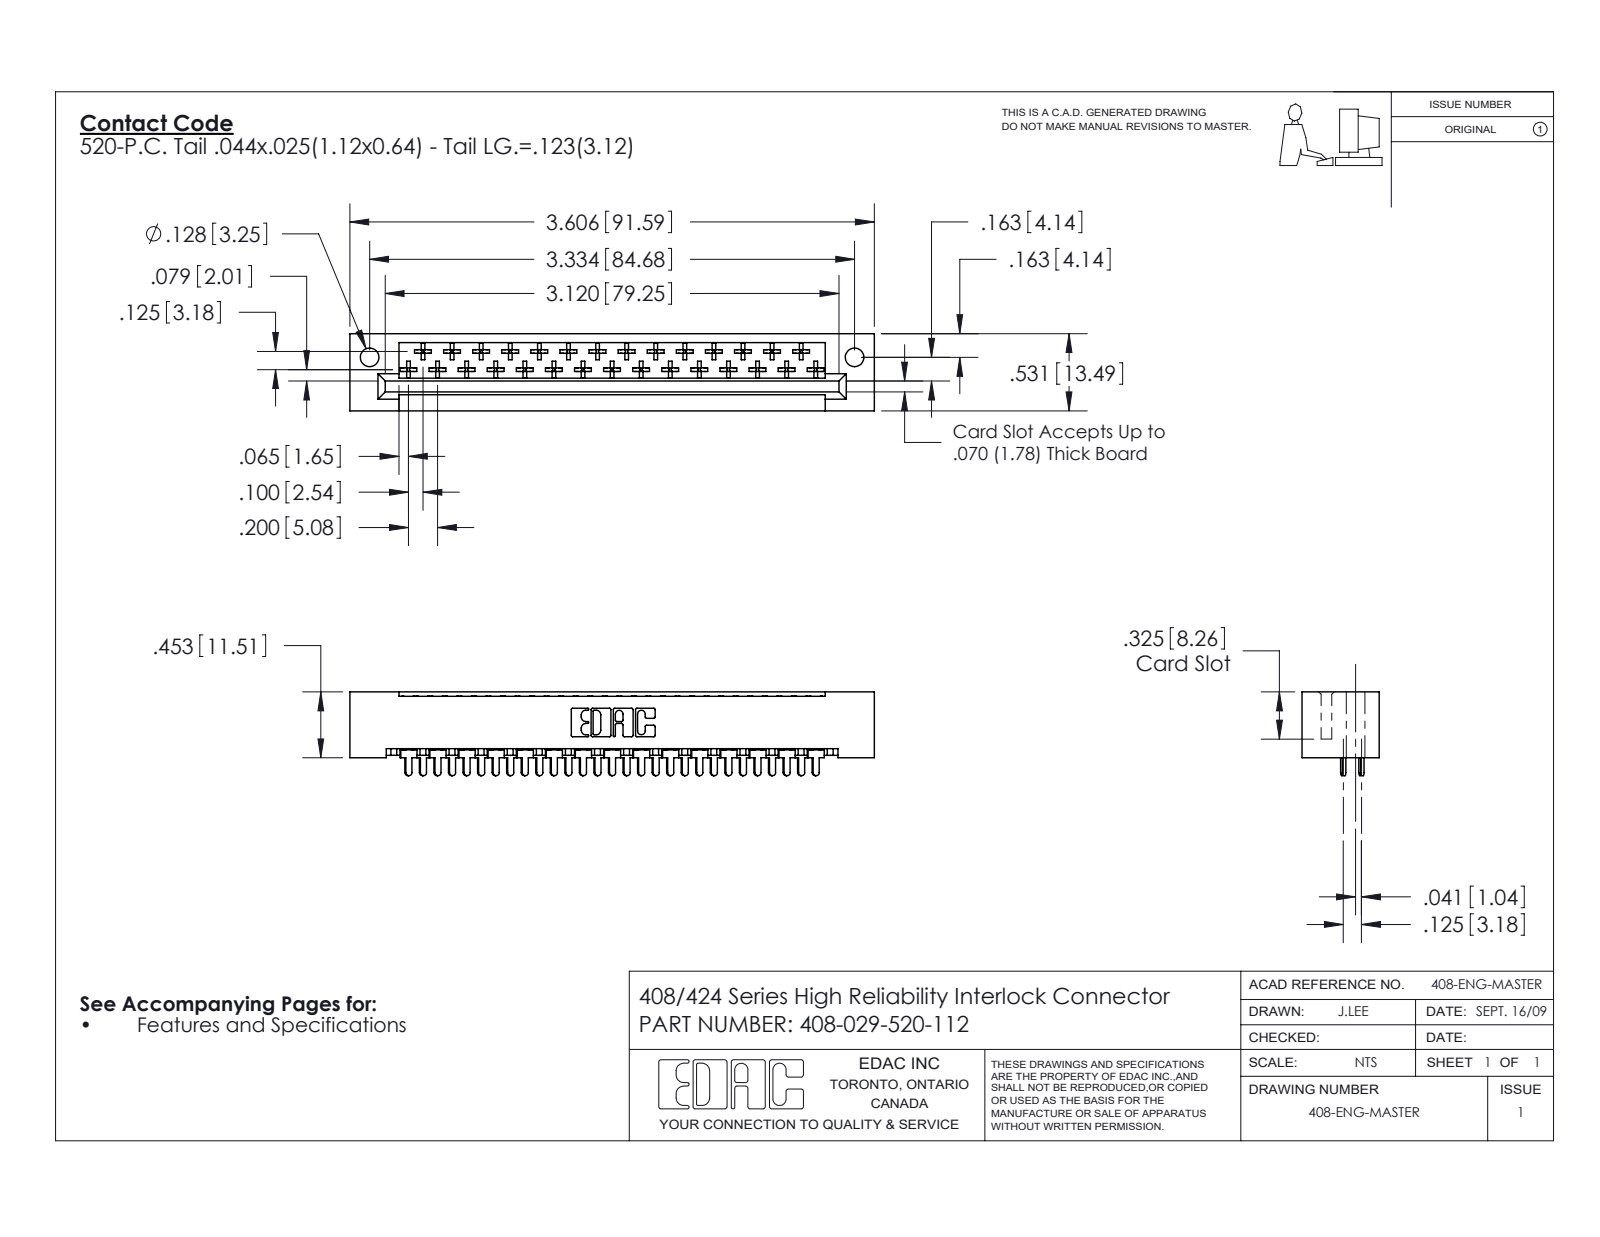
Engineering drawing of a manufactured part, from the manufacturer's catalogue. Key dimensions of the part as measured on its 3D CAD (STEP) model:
Part name (STEP PRODUCT): 408 Part_029 - 1; 408-029-520-112; 408-290-001_408-290-120
STEP written by: SolidWorks 2016 (CONFIG_CONTROL_DESIGN)
Units: inches
Bodies: 30 solids, 1725 faces (1297 planar, 312 cylindrical, 116 other)
Overall size (bounding box): 3.606 × 0.576 × 0.531
Volume: 0.643 in³ · Surface area: 18.95 in²
Round holes (diameter × count): ⌀0.128 ×2
Partial cylindrical surfaces — rounded edges, fillets, slot ends (radius × count): R0.01 ×174, R0.02 ×31, R0.022 ×29, R0.01 ×22, R0.007 ×6, R0.031 ×6, R0.026 ×3
Main face-to-face distances: 0.531, 0.025, 0.4, 0.1, 0.125, 0.025, 0.272, 0.235, 0.259, 0.296
Hole centre spacings: 3.334
